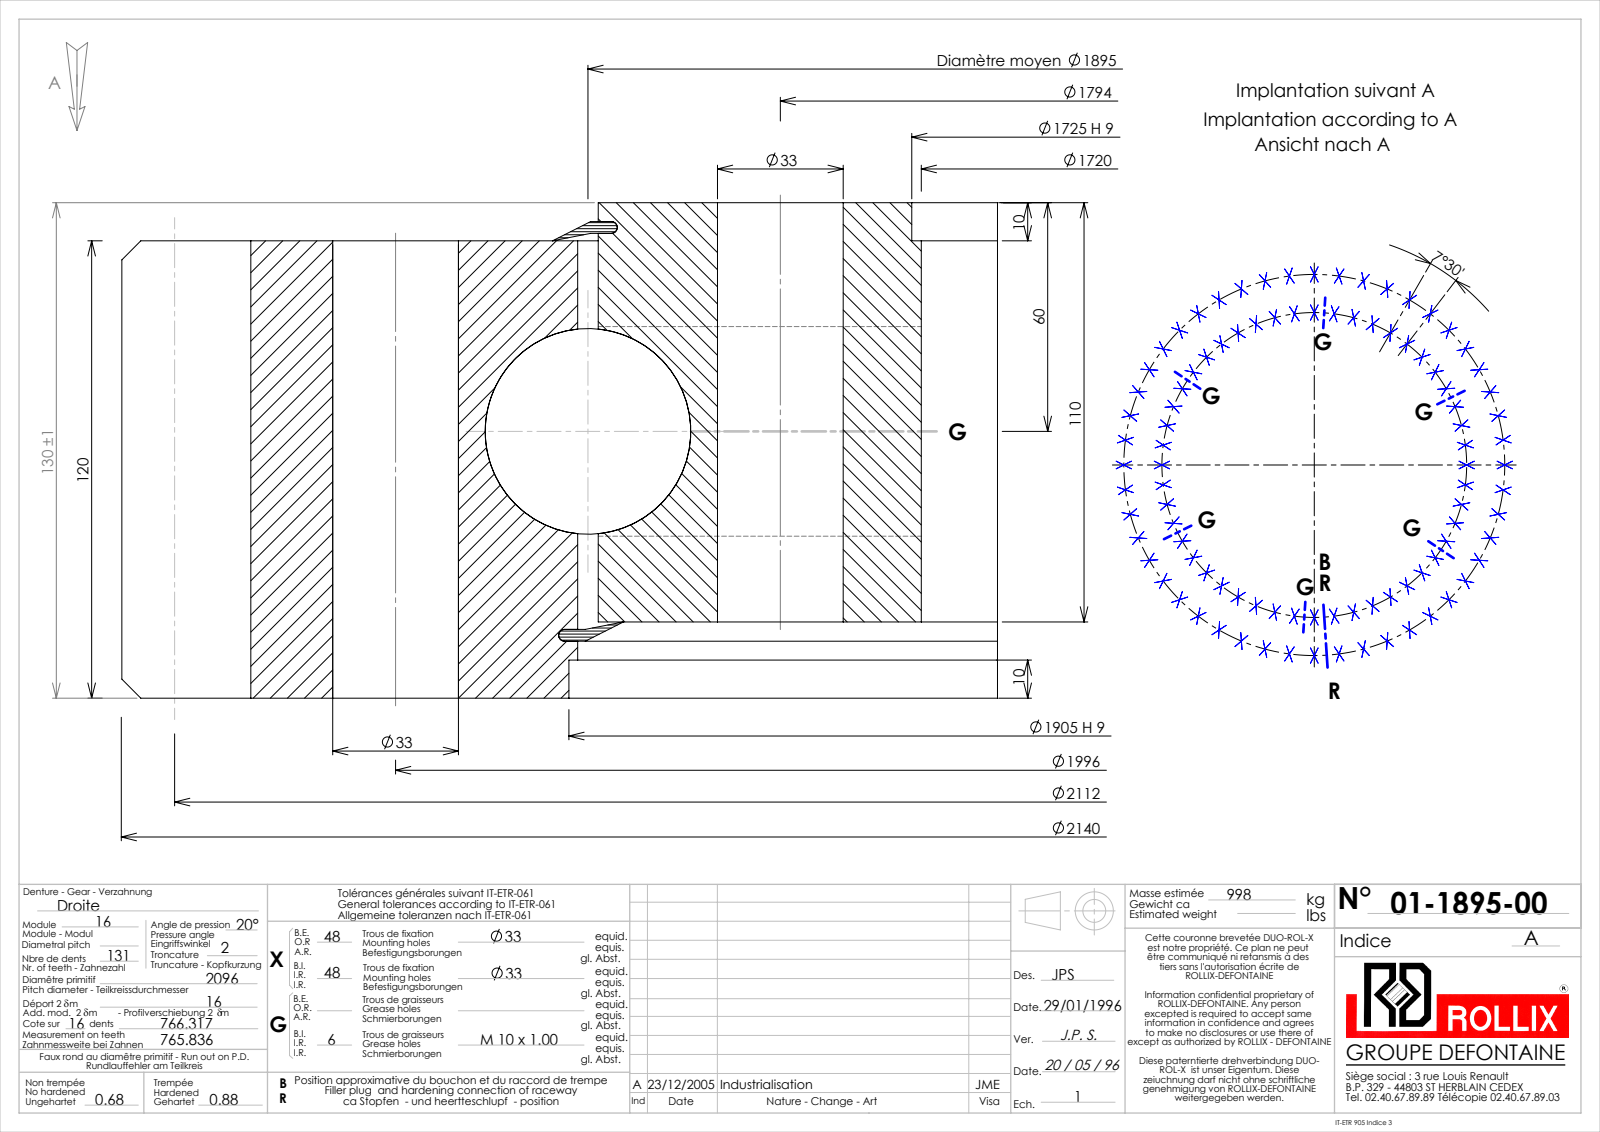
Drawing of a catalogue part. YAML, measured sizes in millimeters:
part_name: "01-1895-00"
step_written_by: "SolidWorks 2016 (CONFIG_CONTROL_DESIGN)"
units: millimeters
bodies: {solids: 5, faces: 1052, planar: 276, cylindrical: 485, other: 291}
overall_size: [2139.98, 2139.85, 130]
volume: 110400000
surface_area: 7625000
round_holes:
  - {diameter: 33, count: 96}
  - {diameter: 9, count: 6}
  - {diameter: 1720, count: 1}
  - {diameter: 1725, count: 1}
  - {diameter: 1900.4, count: 1}
  - {diameter: 1905, count: 1}
round_bosses_or_shafts:
  - {diameter: 1889.6, count: 1}
partial_cylinders:
  - {radius: 1036, count: 1}
  - {radius: 1070, count: 1}
face_to_face_distances: [120, 10, 110, 20, 100, 130, 1.95, 101.95, 5.05, 105.05]
hole_center_spacings: [389.4, 260.53, 641.59, 130.55, 998, 1316.05, 1500.67, 1659.61]
